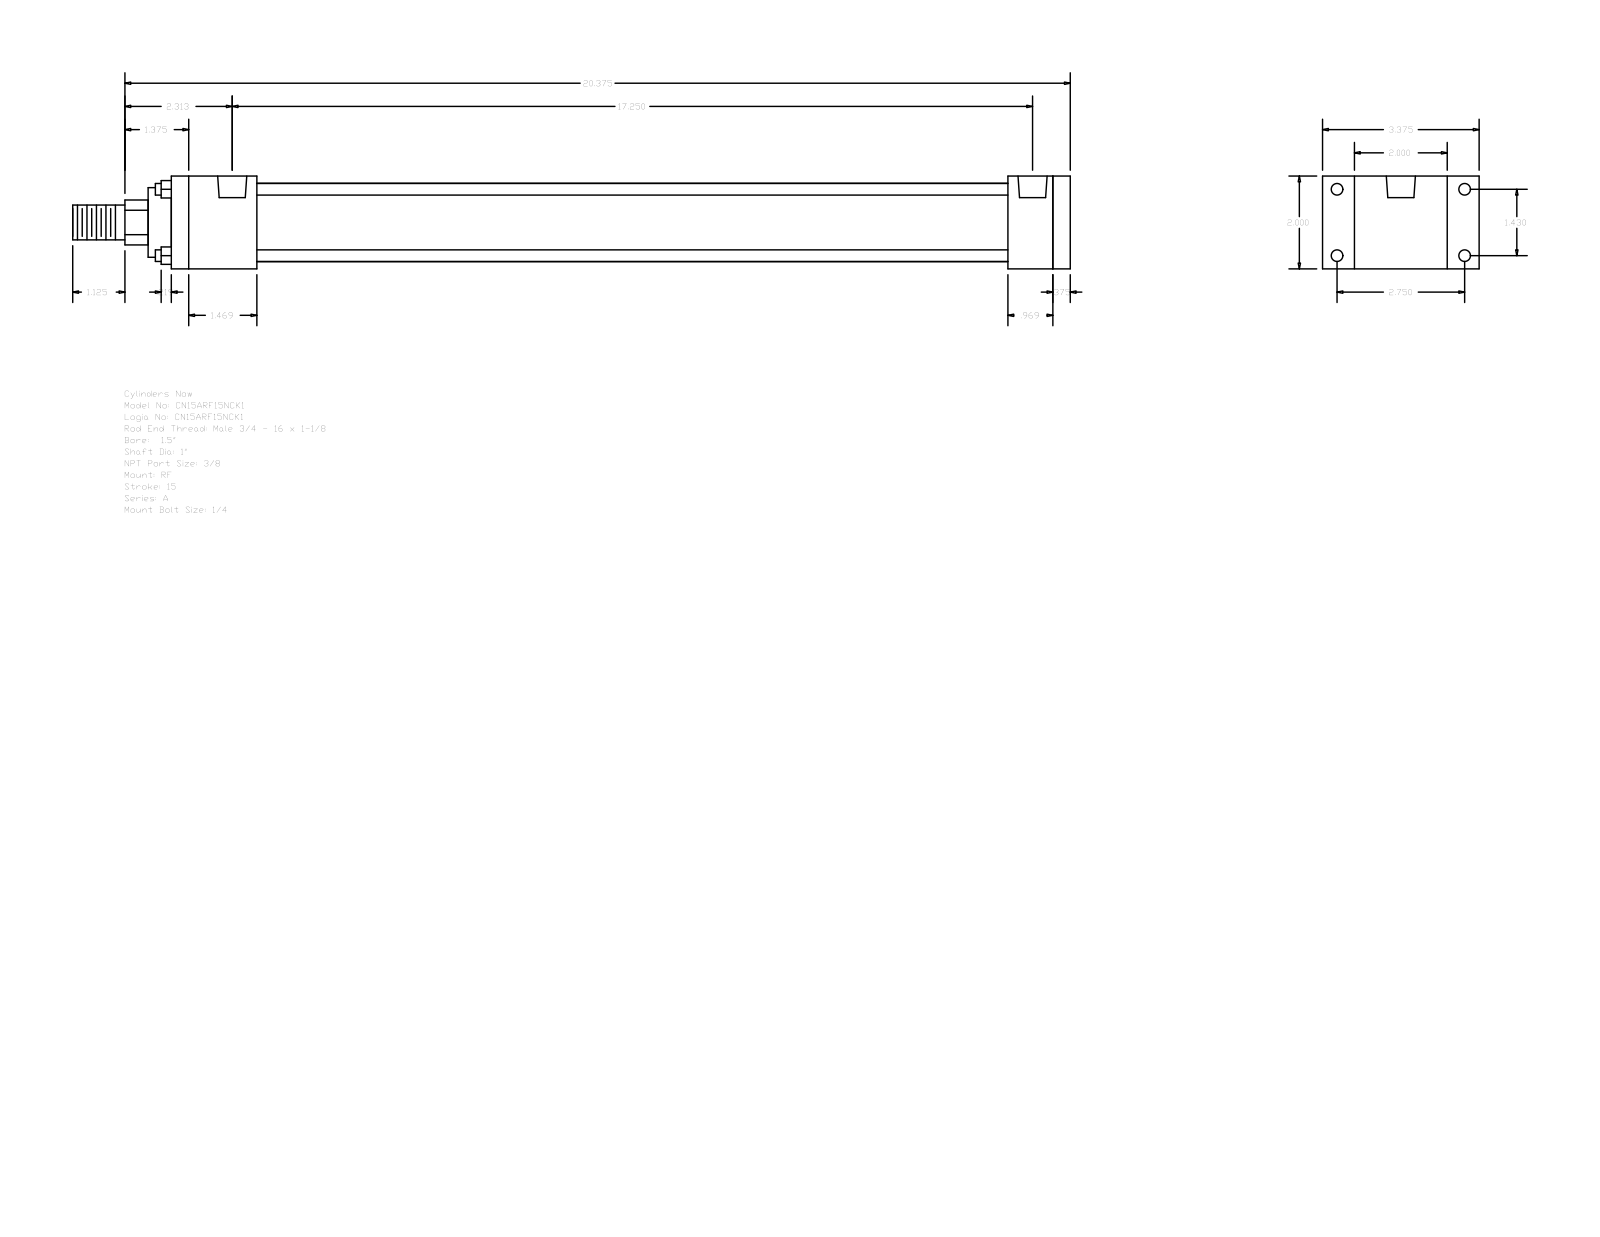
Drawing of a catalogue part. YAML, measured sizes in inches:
part_name: "A_RF__0150_1"
step_written_by: "GSSL Pune (CONFIG_CONTROL_DESIGN)"
units: inches
bodies: {solids: 0, faces: 92, planar: 64, cylindrical: 28, other: 0}
overall_size: [21.5, 3.375, 2]
round_holes:
  - {diameter: 0.219, count: 4}
  - {diameter: 0.25, count: 4}
  - {diameter: 0.627, count: 2}
round_bosses_or_shafts:
  - {diameter: 0.25, count: 4}
  - {diameter: 1.69, count: 1}
  - {diameter: 1.5, count: 1}
  - {diameter: 1, count: 1}
  - {diameter: 0.75, count: 1}
partial_cylinders:
  - {radius: 0.484, count: 1}
face_to_face_distances: [2, 0.375, 19, 19.375, 18.031, 0.969, 1.344, 1.844, 16.187, 17.156]
hole_center_spacings: [0.156, 1.43, 2.75, 3.099, 16.937, 17.094, 17.25]
